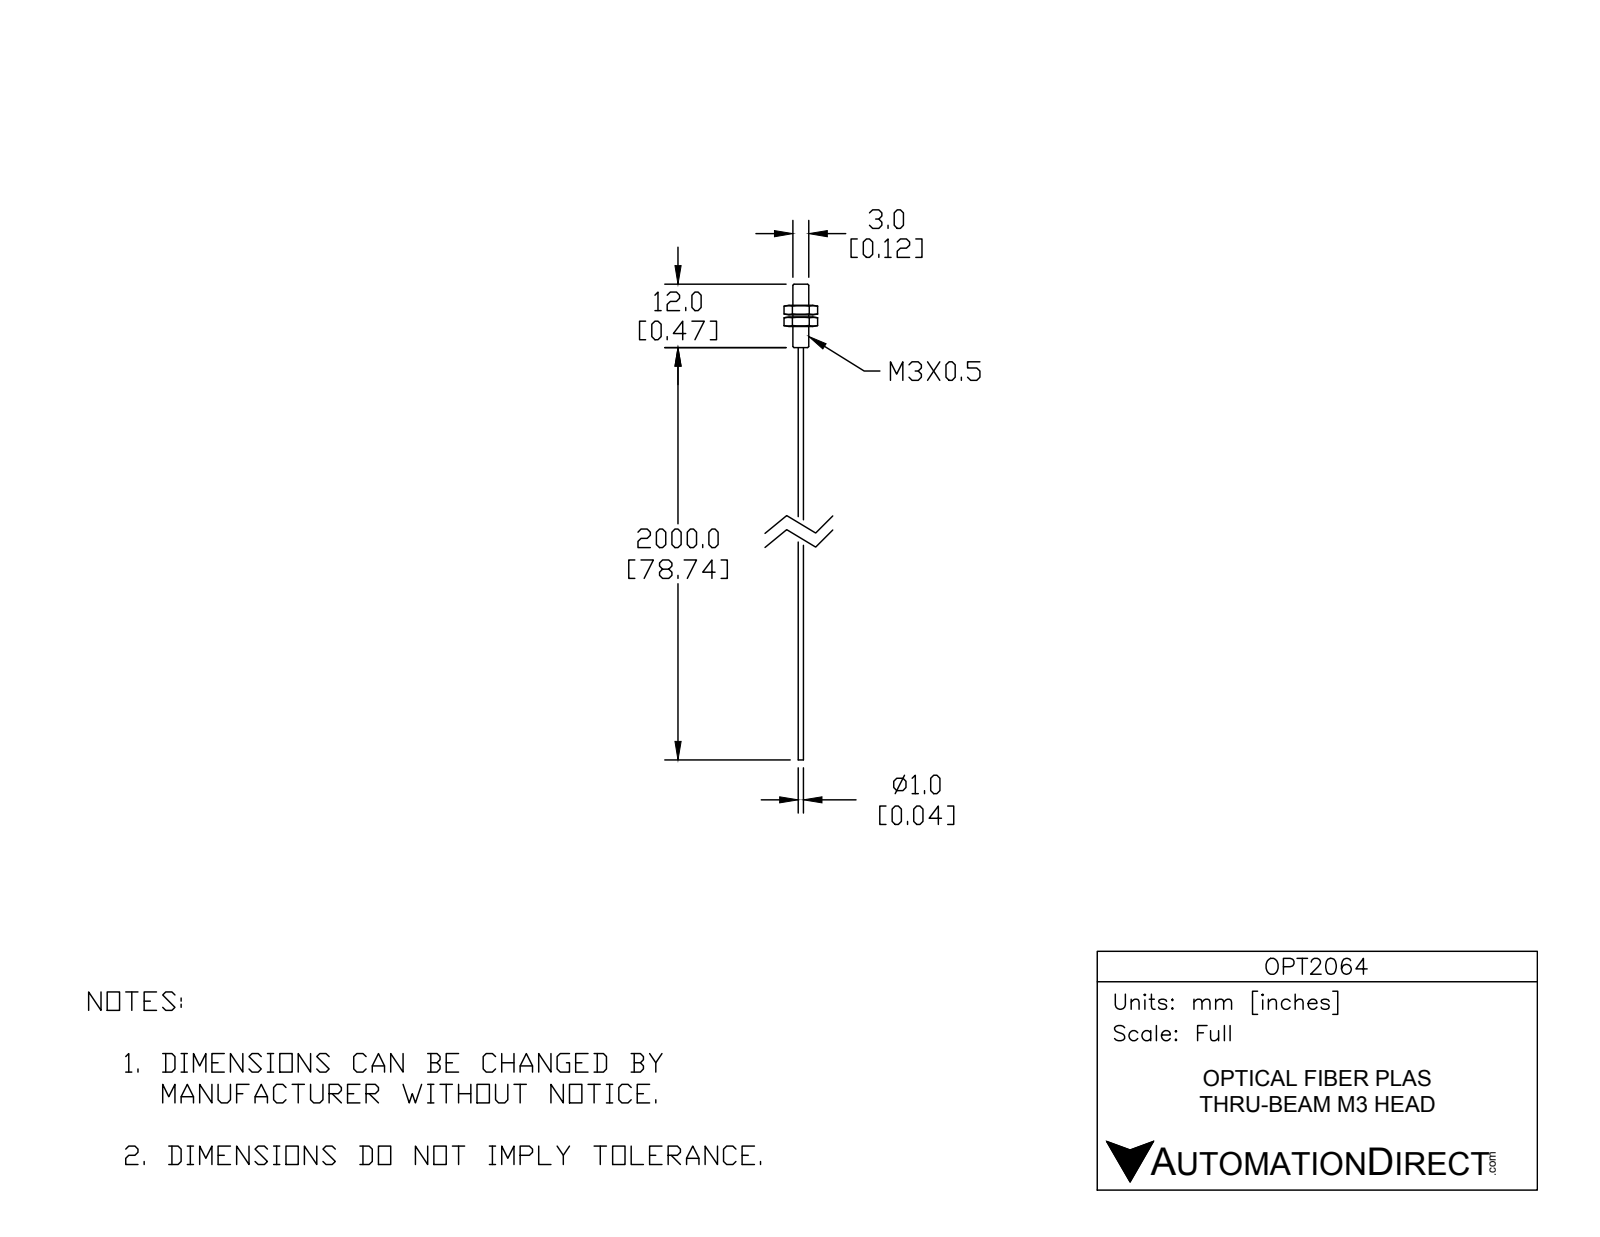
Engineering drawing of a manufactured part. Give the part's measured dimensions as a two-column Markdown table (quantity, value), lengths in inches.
| quantity | value |
| --- | --- |
| part name | OPT2064 |
| STEP written by | SolidWorks 2014 (AUTOMOTIVE_DESIGN) |
| units | inches |
| bodies | 2 solids, 43 faces (21 planar, 10 cylindrical, 12 other) |
| overall size | 3.543 × 0.25 × 0.217 |
| volume | 0.013 in³ |
| surface area | 0.702 in² |
| round bosses / shafts (diameter × count) | 0.118 × 1, 0.039 × 1 |
| main face-to-face distances | 0.217, 0.157, 0.071, 0.087, 0.228, 0.244, 0.315, 0.016, 0.472, 0.259 |
